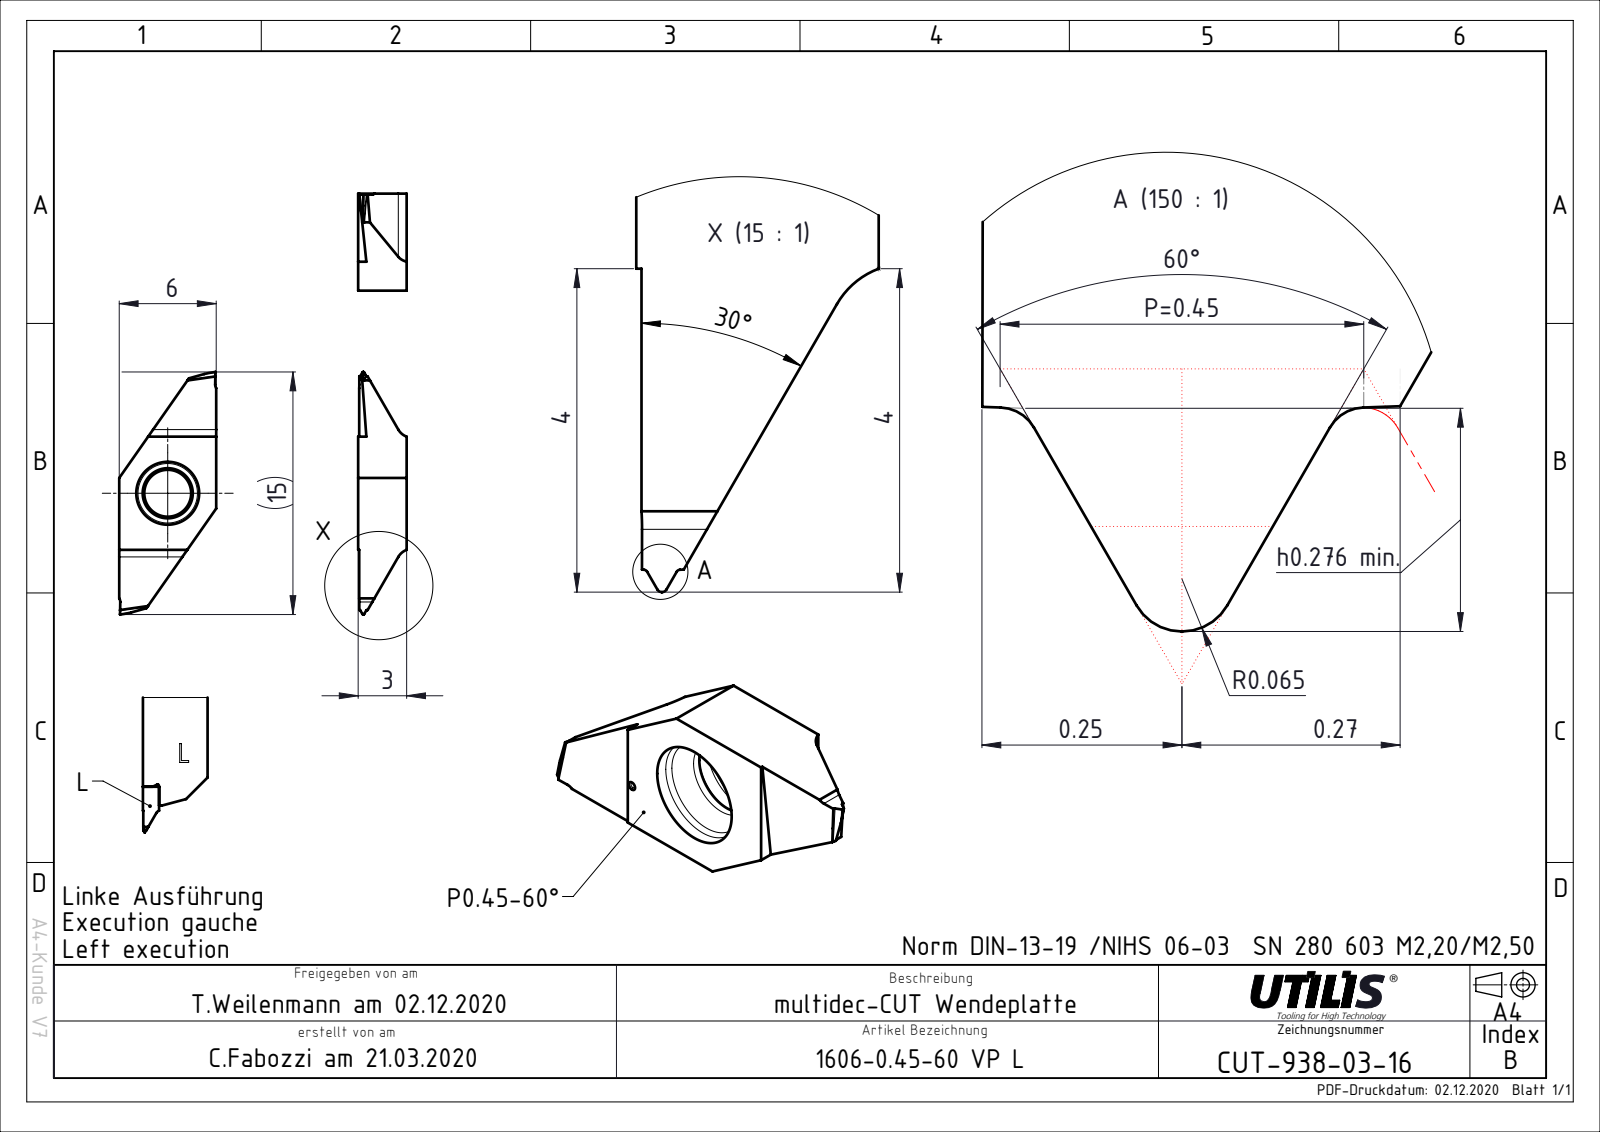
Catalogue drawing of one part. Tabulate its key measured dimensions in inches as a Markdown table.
| quantity | value |
| --- | --- |
| part name | CUT-938-03; ASME Y14.5 |
| STEP written by | FormatWorks Professional (AP242_MANAGED_MODEL_BASED_3D_ENGINEERING_MIM_LF) |
| units | inches |
| bodies | 1 solid, 40 faces (22 planar, 14 cylindrical, 4 other) |
| overall size | 0.591 × 0.236 × 0.118 |
| volume | 0.008 in³ |
| surface area | 0.329 in² |
| round holes (diameter × count) | 0.114 × 1 |
| partial cylindrical surfaces (radius × count) | 0.039 × 2 |
| main face-to-face distances | 0.236, 0.118, 0.354, 0.44, 0.472, 0.276, 0.511, 0.511 |
